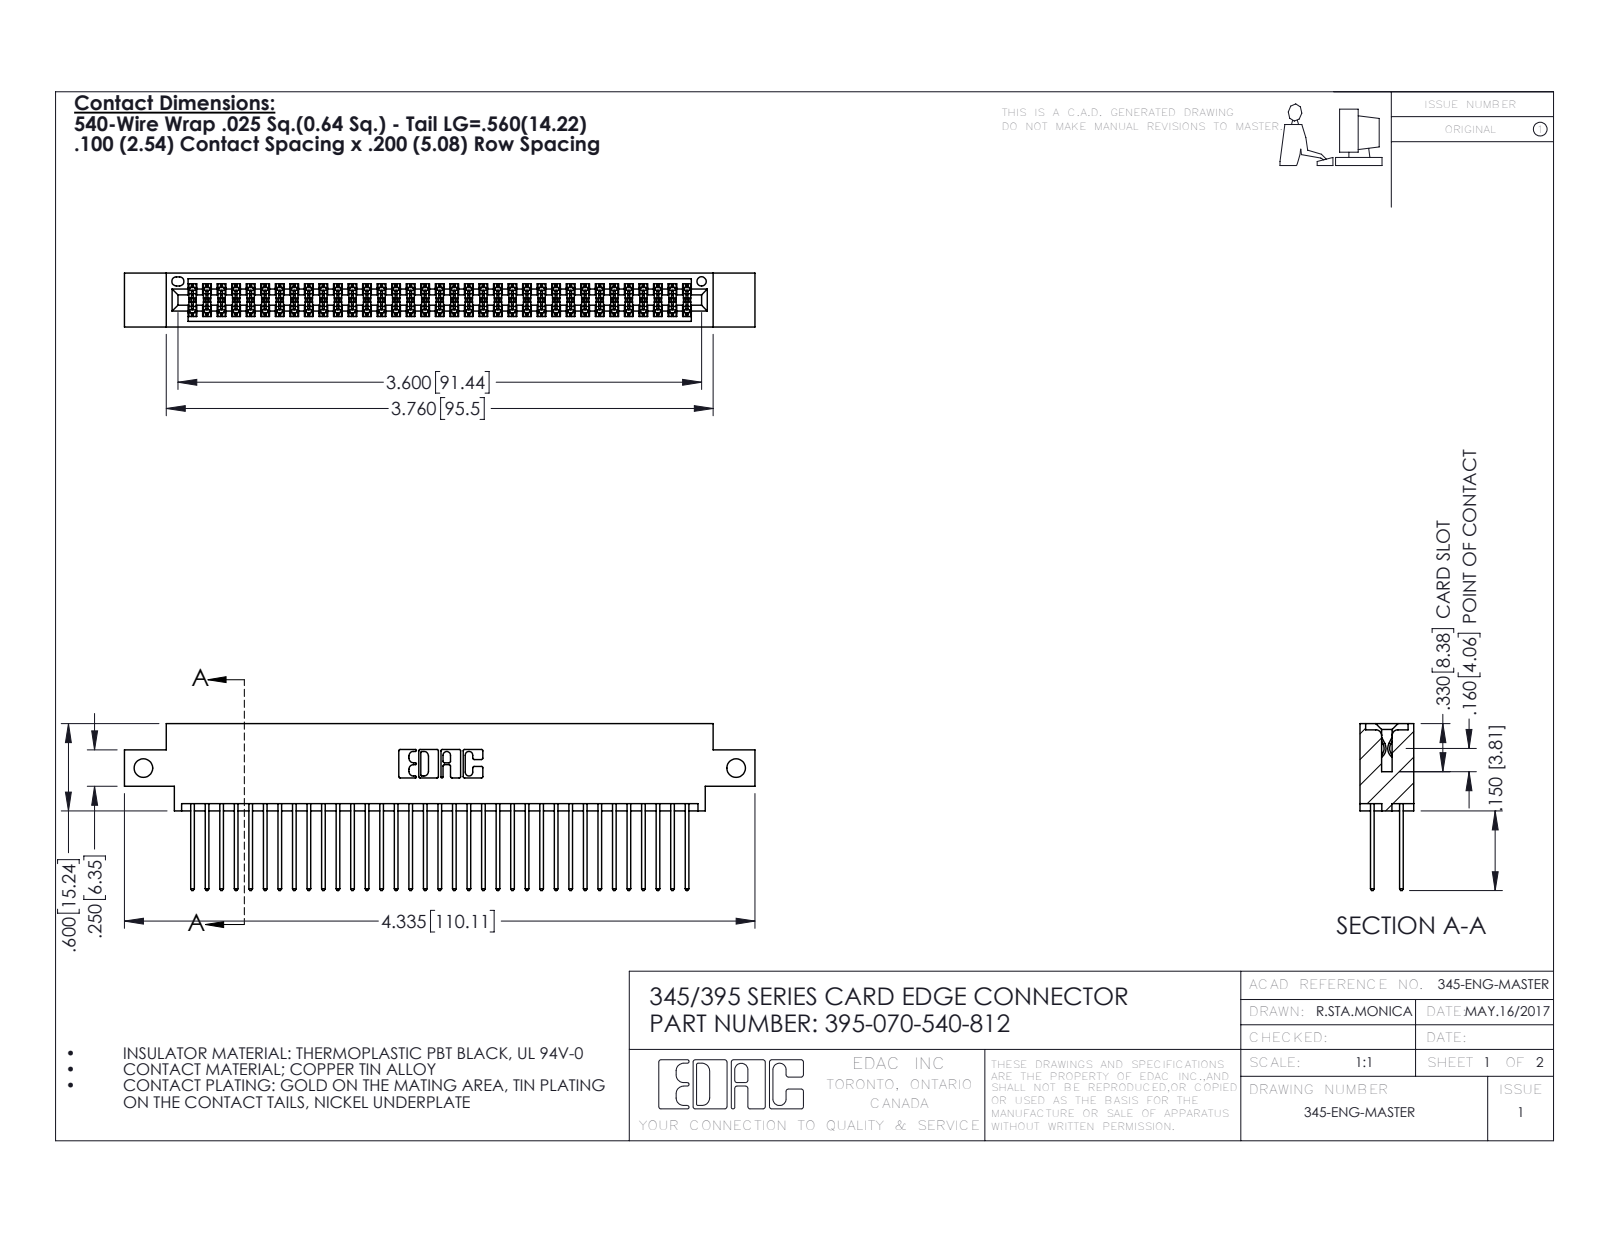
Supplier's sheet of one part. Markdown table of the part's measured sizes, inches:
| quantity | value |
| --- | --- |
| part name | 395-070-540-812; 345 Part_0.170 Offset - Side Mount; 345-292-001_345-293-140 |
| STEP written by | SolidWorks 2016 (CONFIG_CONTROL_DESIGN) |
| units | inches |
| bodies | 71 solids, 3630 faces (2394 planar, 1236 cylindrical, 0 other) |
| overall size | 4.335 × 1.147 × 0.37 |
| volume | 0.653 in³ |
| surface area | 26.22 in² |
| round holes (diameter × count) | 0.128 × 2, 0.064 × 1 |
| partial cylindrical surfaces (radius × count) | 0.006 × 105, 0.01 × 70, 0.01 × 22, 0.007 × 6, 0.031 × 6, 0.026 × 3, 0.014 × 2, 0.019 × 2 |
| main face-to-face distances | 0.298, 0.072, 0.2, 0.098, 0.272, 0.025, 0.37, 0.225, 0.175, 0.149 |
| hole center spacings | 4.075 |
